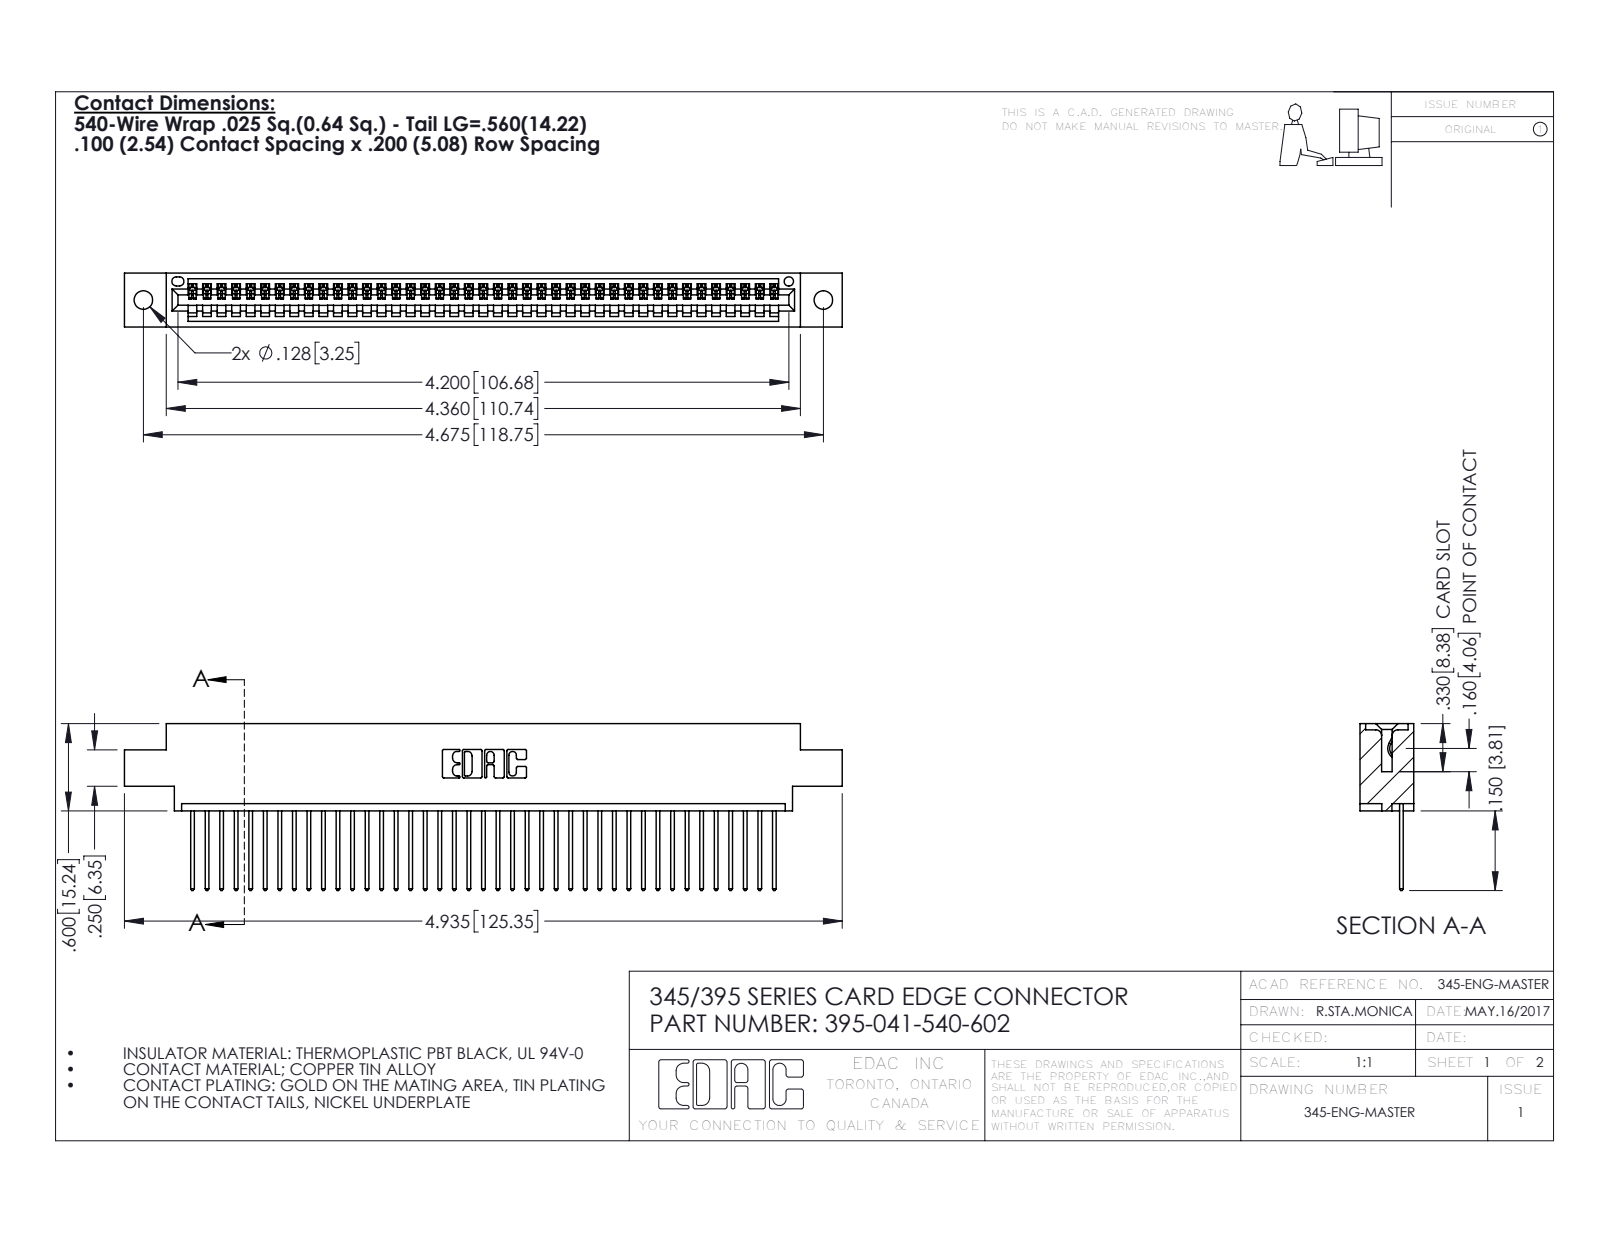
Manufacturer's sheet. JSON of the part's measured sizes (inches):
{"part_name": "345 Part_0.170 Offset - 0.128 Dia; 345-292-001_345-293-140; 395-041-540-602", "step_written_by": "SolidWorks 2016 (CONFIG_CONTROL_DESIGN)", "units": "inches", "bodies": {"solids": 42, "faces": 2508, "planar": 1724, "cylindrical": 784, "other": 0}, "overall_size": [4.935, 1.147, 0.37], "volume_in3": 0.72, "surface_area_in2": 24.69, "round_holes": [[0.128, 2], [0.064, 1]], "partial_cylinders_radius": [[0.006, 82], [0.01, 82], [0.01, 22], [0.007, 6], [0.031, 6], [0.026, 3], [0.031, 2], [0.04, 2]], "face_to_face_distances": [0.298, 0.072, 0.37, 0.098, 0.272, 0.025, 0.2, 0.225, 0.175, 0.149], "hole_center_spacings": [0.27, 4.439, 4.675]}
